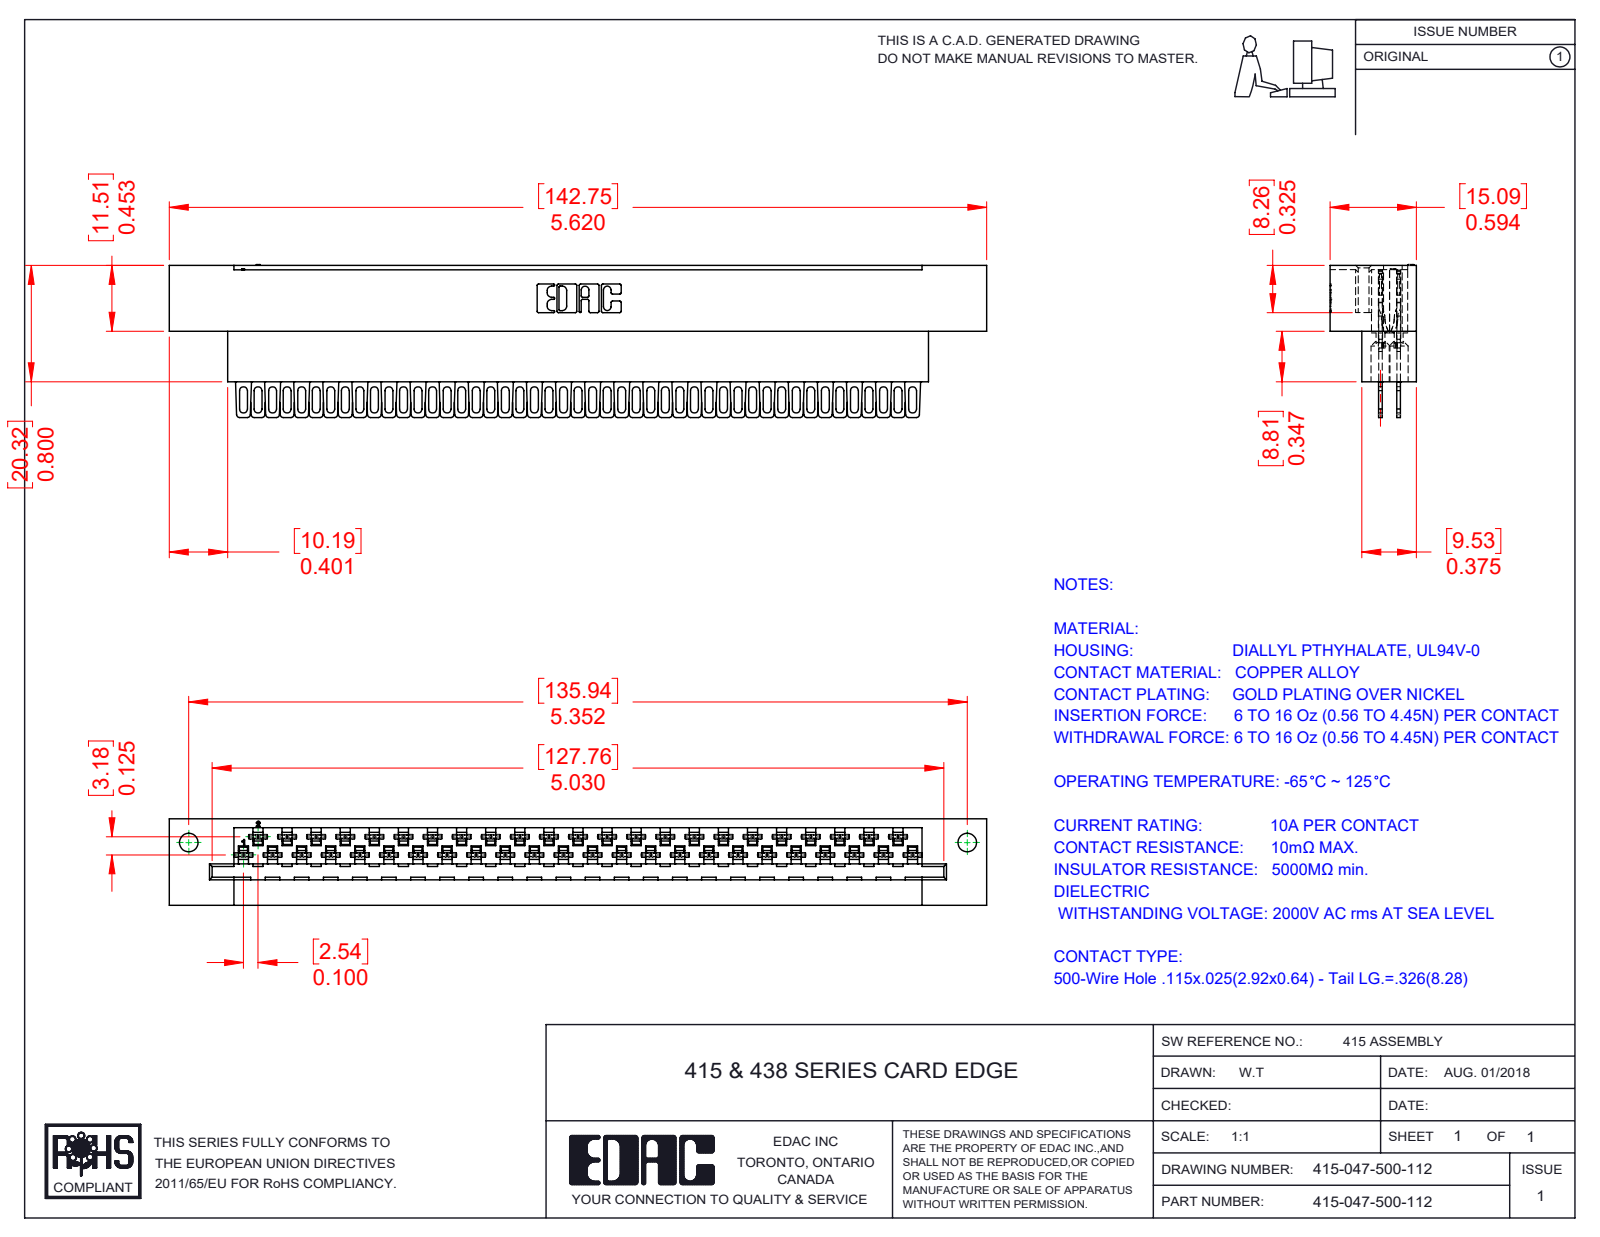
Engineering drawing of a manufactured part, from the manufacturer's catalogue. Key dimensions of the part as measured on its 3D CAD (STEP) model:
Part name (STEP PRODUCT): 415-210-001_415-210-047-112; 415-047-500-112; 516-290-001_500
STEP written by: SolidWorks 2016 (CONFIG_CONTROL_DESIGN)
Units: millimetres
Bodies: 48 solids, 4938 faces (3086 planar, 1407 cylindrical, 445 other)
Overall size (bounding box): 142.75 × 26.68 × 15.09
Volume: 26 638 mm³ · Surface area: 30 817 mm²
Round holes (diameter × count): ⌀1.27 ×47, ⌀3.3 ×47, ⌀3.25 ×2
Partial cylindrical surfaces — rounded edges, fillets, slot ends (radius × count): R0.3 ×188, R0.56 ×188, R0.18 ×94, R0.2 ×94, R0.41 ×94, R0.51 ×94, R0.69 ×94, R2.03 ×94
Main face-to-face distances: 3.18, 0.61, 1.88, 1.27, 15.09, 1.94, 0.67, 6.61, 8.48, 6
Hole centre spacings: 5.08, 10.16, 15.24, 20.32, 25.4, 30.48, 35.56, 2.54
